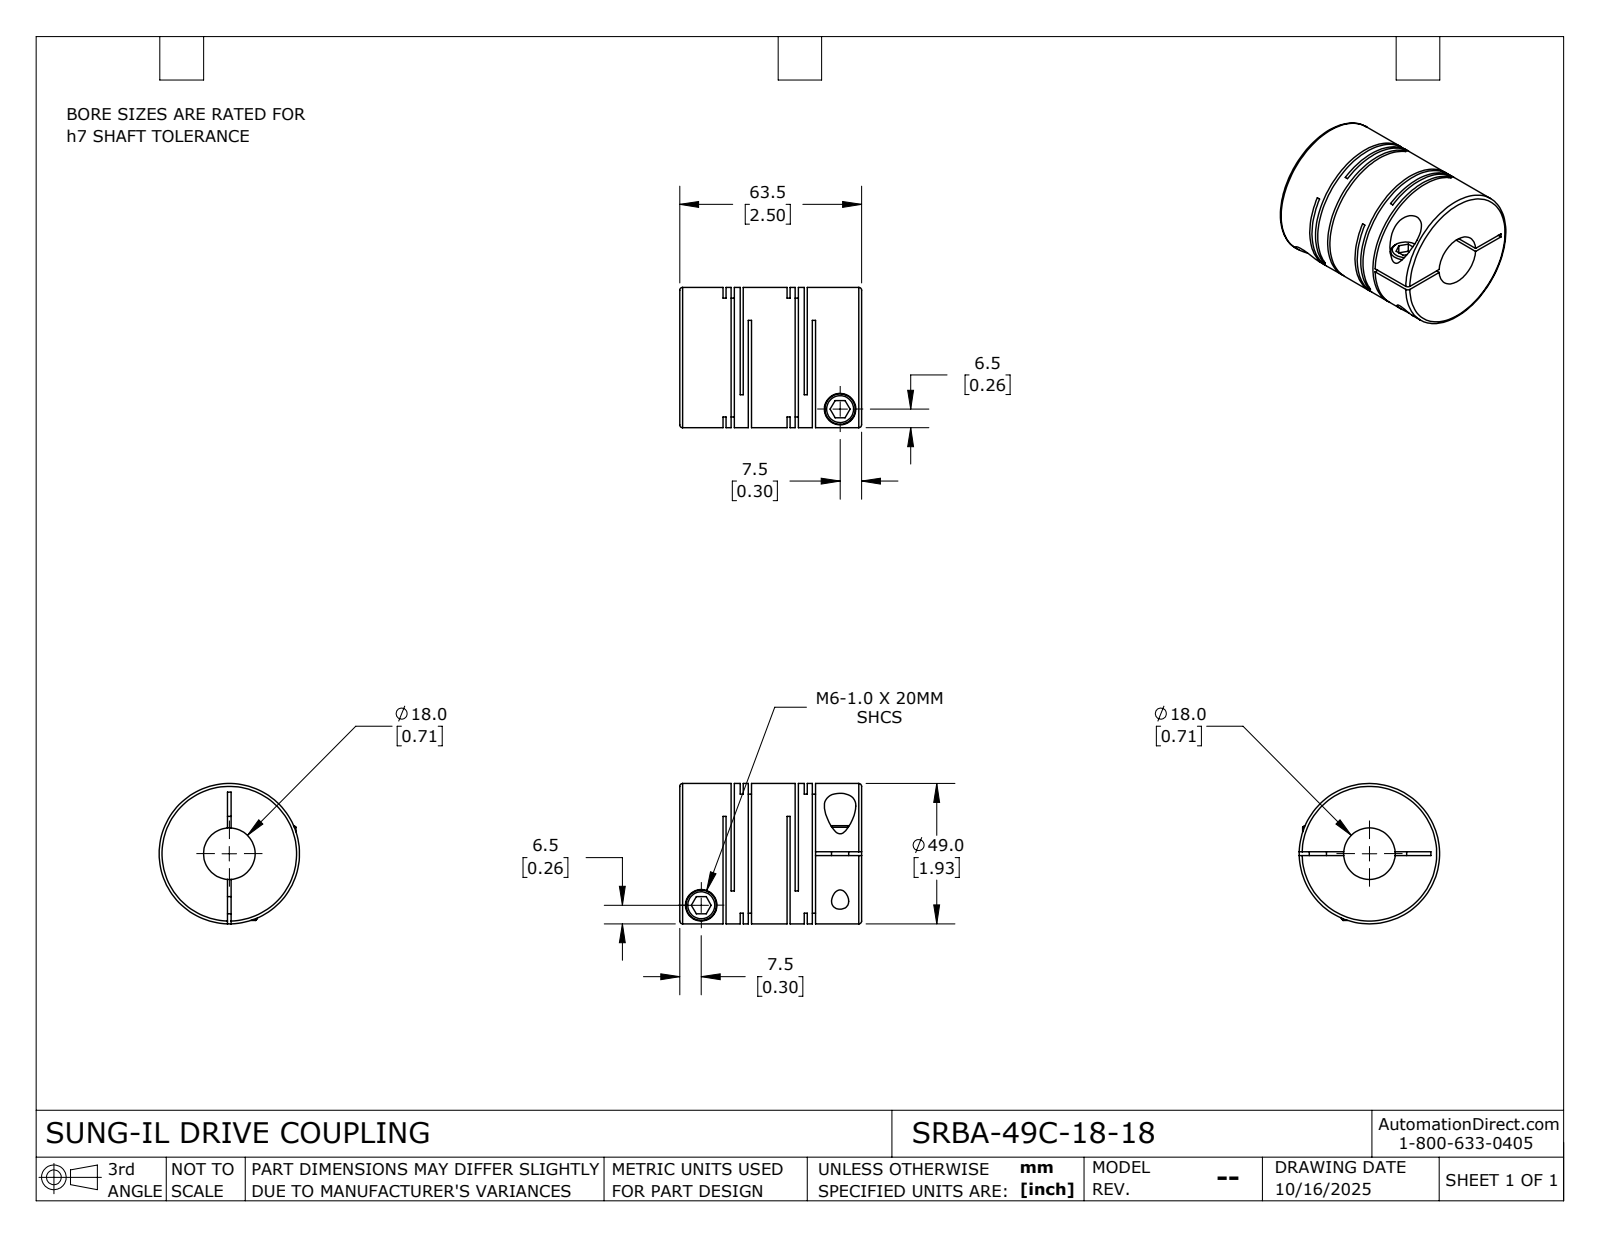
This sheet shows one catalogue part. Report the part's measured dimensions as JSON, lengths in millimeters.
{"part_name": "SRBA-49C-18-18", "step_written_by": "SolidWorks 2024 (CONFIG_CONTROL_DESIGN)", "units": "millimeters", "bodies": {"solids": 1, "faces": 115, "planar": 60, "cylindrical": 42, "other": 13}, "overall_size": [63.5, 49, 49], "volume_mm3": 89393, "surface_area_mm2": 38820, "round_holes": [[6, 2], [11, 2], [18, 1]], "round_bosses_or_shafts": [[10.6, 2], [49, 1]], "face_to_face_distances": [6, 1.1, 22.35, 2.85, 21.25, 3.15, 19.5, 16.35, 1.75, 4.9]}
